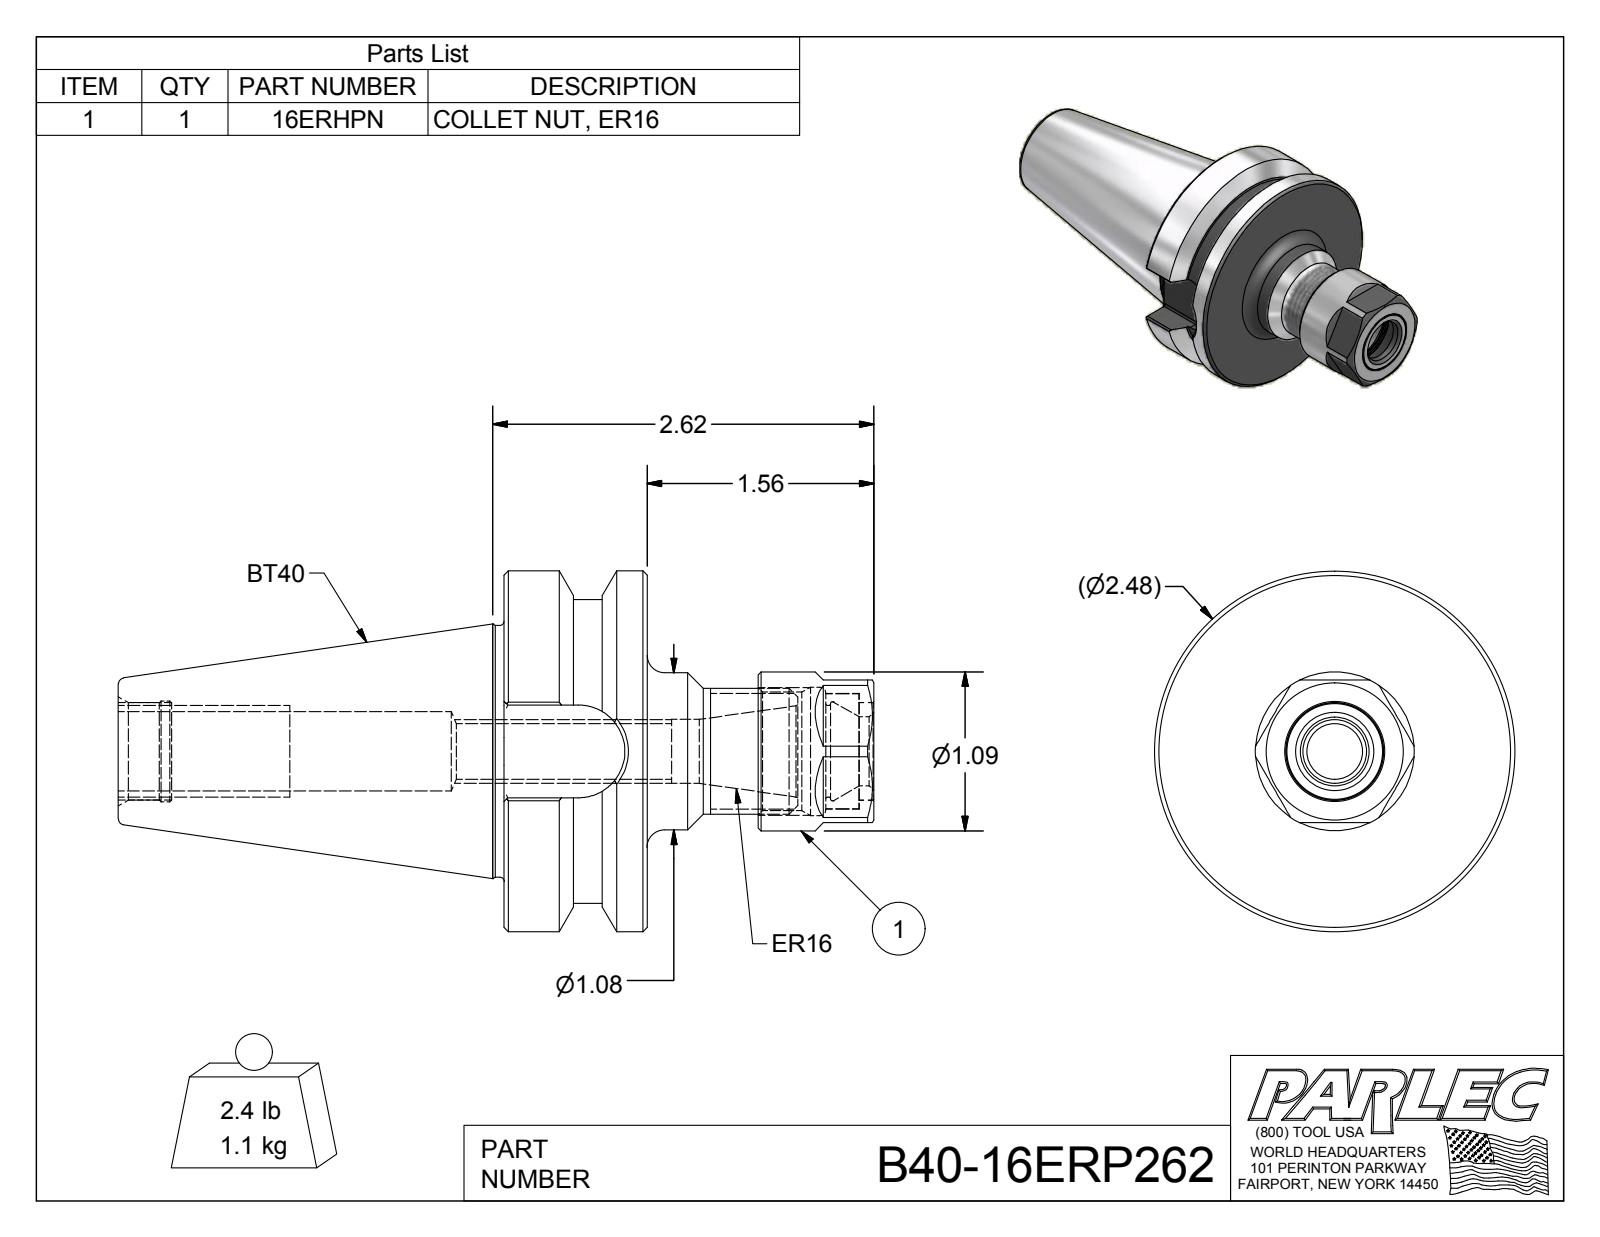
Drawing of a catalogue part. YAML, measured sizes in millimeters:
part_name: "B40-16ERP262; B40-16ER2-1; 16ERHPN"
step_written_by: "Autodesk Inventor 2012 (AUTOMOTIVE_DESIGN)"
units: millimeters
bodies: {solids: 3, faces: 116, planar: 45, cylindrical: 34, other: 37}
overall_size: [132, 63, 63]
volume: 137500
surface_area: 30370
round_holes:
  - {diameter: 9.7, count: 1}
  - {diameter: 11.2, count: 1}
  - {diameter: 12, count: 1}
  - {diameter: 13.8, count: 1}
  - {diameter: 16, count: 1}
  - {diameter: 17, count: 1}
  - {diameter: 17.1, count: 1}
  - {diameter: 17.3, count: 1}
  - {diameter: 17.6, count: 1}
  - {diameter: 20.2, count: 1}
  - {diameter: 20.7, count: 1}
  - {diameter: 22.4, count: 1}
round_bosses_or_shafts:
  - {diameter: 63, count: 1}
  - {diameter: 53, count: 1}
  - {diameter: 43.9, count: 1}
  - {diameter: 27.7, count: 1}
  - {diameter: 27.4, count: 1}
  - {diameter: 22, count: 1}
  - {diameter: 20.1, count: 1}
  - {diameter: 17, count: 1}
partial_cylinders:
  - {radius: 0.5, count: 8}
  - {radius: 8.1, count: 1}
face_to_face_distances: [25, 24.9, 45.2, 64.6, 39.6, 67.4, 92.4, 132, 4.4, 20.5]
